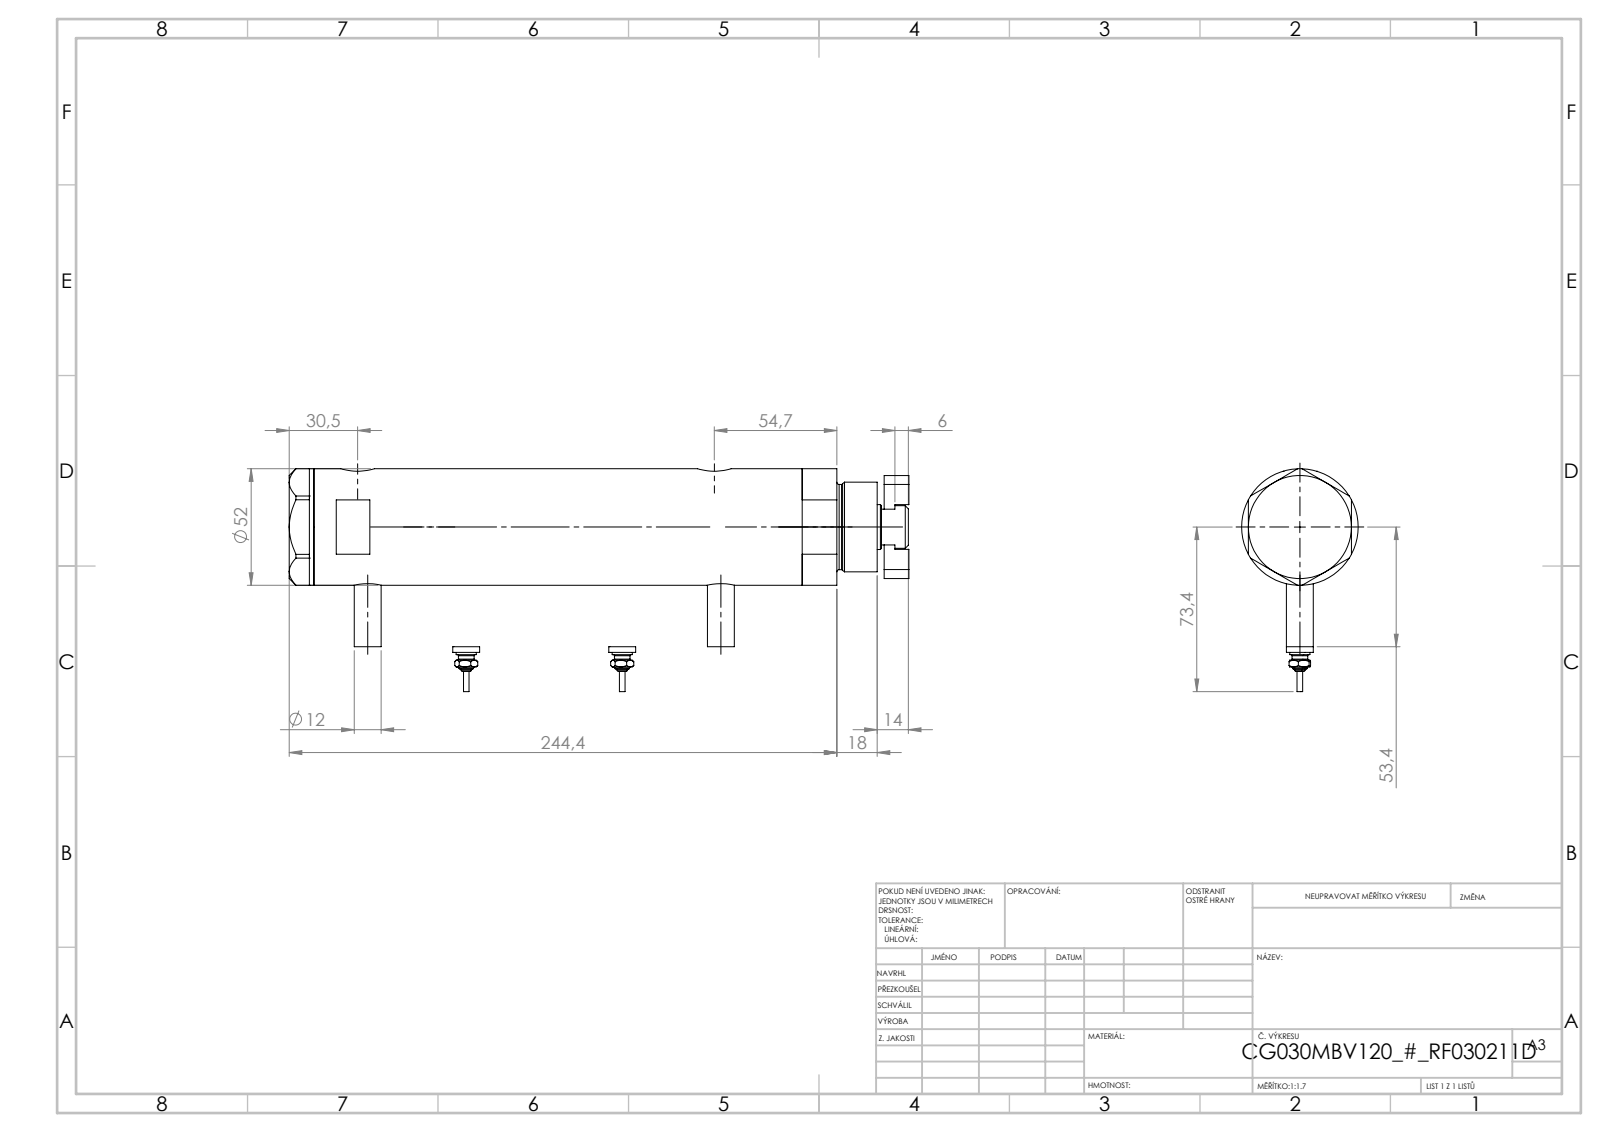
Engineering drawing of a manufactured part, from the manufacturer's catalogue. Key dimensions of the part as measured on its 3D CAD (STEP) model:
Part name (STEP PRODUCT): V270CG_VC; V270CG_BACK; Switch; V270CG_MIDDLE (+2 more)
STEP written by: SolidWorks 2019 (CONFIG_CONTROL_DESIGN)
Units: millimetres
Bodies: 8 solids, 266 faces (117 planar, 85 cylindrical, 64 other)
Overall size (bounding box): 276.5 × 99.4 × 52
Volume: 502 346 mm³ · Surface area: 112 351 mm²
Round holes (diameter × count): ⌀5.1 ×4, ⌀9 ×4, ⌀9.73 ×2, ⌀12.5 ×2, ⌀15 ×2, ⌀6.5 ×1, ⌀20 ×1, ⌀21.5 ×1, ⌀30 ×1, ⌀33 ×1, ⌀44 ×1
Round bosses / shafts (diameter × count): ⌀12 ×4, ⌀9 ×2, ⌀7 ×2, ⌀4.5 ×2, ⌀2.5 ×2, ⌀52 ×1, ⌀40 ×1, ⌀38 ×1
Main face-to-face distances: 11, 181.5, 23.8, 157.7, 34.8, 192.5, 46, 33.5, 36.4, 228.9
Hole centre spacings: 16.74, 10, 31.96, 33.49, 2.9, 4.5, 154.7, 157.6
